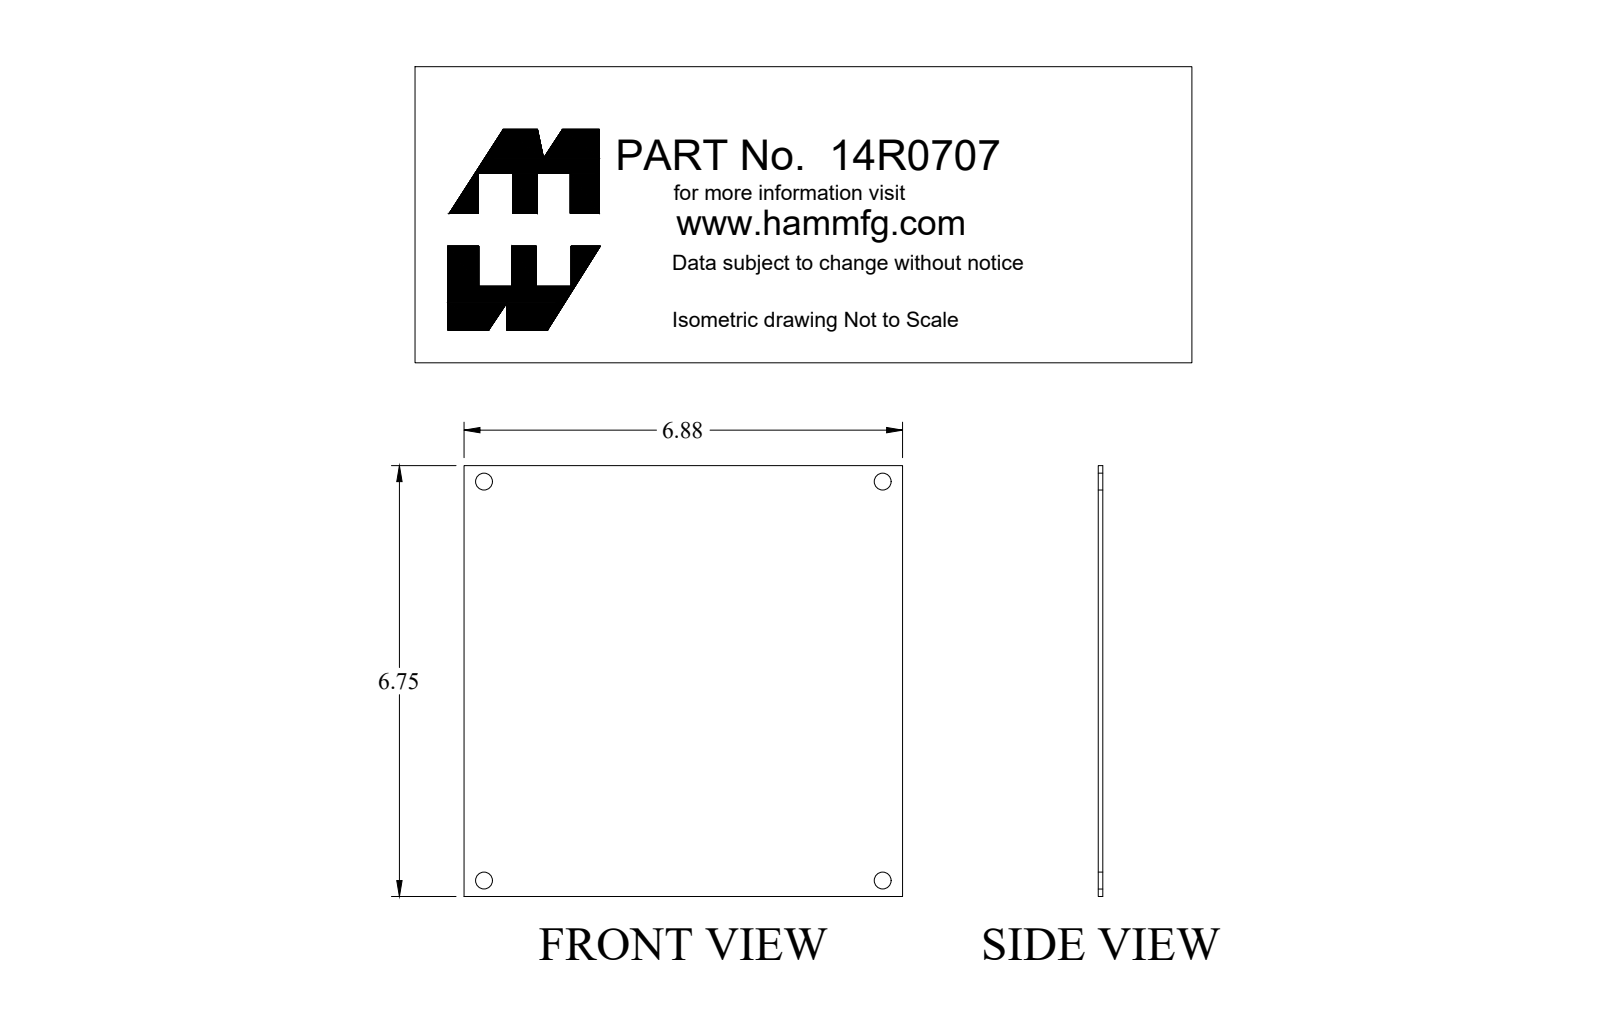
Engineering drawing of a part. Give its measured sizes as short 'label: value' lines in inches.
name: 14R0707
written by: SolidWorks 2018 (AUTOMOTIVE_DESIGN)
unit: in
bodies: 1 solid, 10 faces (6 planar, 4 cylindrical, 0 other)
size: 6.875 × 6.75 × 0.072
volume: 3.325 in³; area: 94.57 in²
holes: 4× ⌀0.265
face distances: 0.072, 6.75, 6.875
hole spacings: 6.25, 8.839
